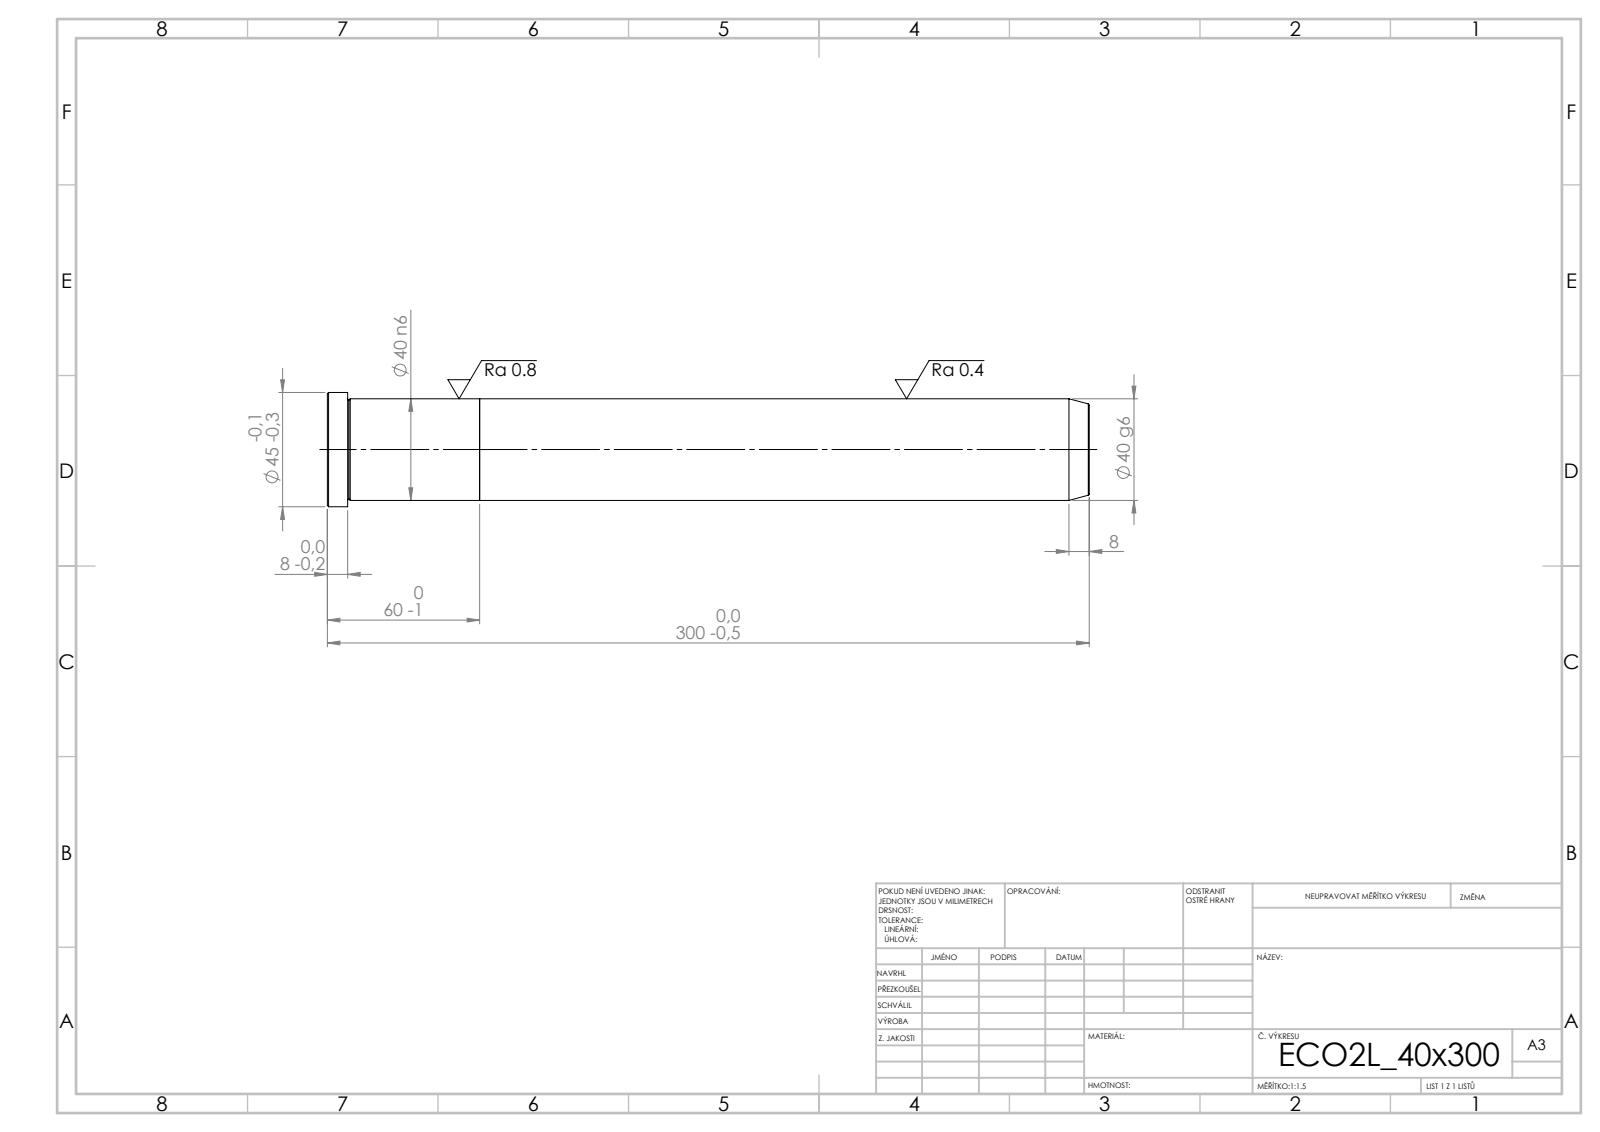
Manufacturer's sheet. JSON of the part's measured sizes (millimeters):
{"step_written_by": "SolidWorks 2019 (CONFIG_CONTROL_DESIGN)", "units": "millimeters", "bodies": {"solids": 2, "faces": 21, "planar": 5, "cylindrical": 6, "other": 10}, "overall_size": [300, 45, 45], "volume_mm3": 378553, "surface_area_mm2": 43258, "round_bosses_or_shafts": [[45, 1], [40, 1]], "face_to_face_distances": [60, 240, 300, 292, 52, 8]}
